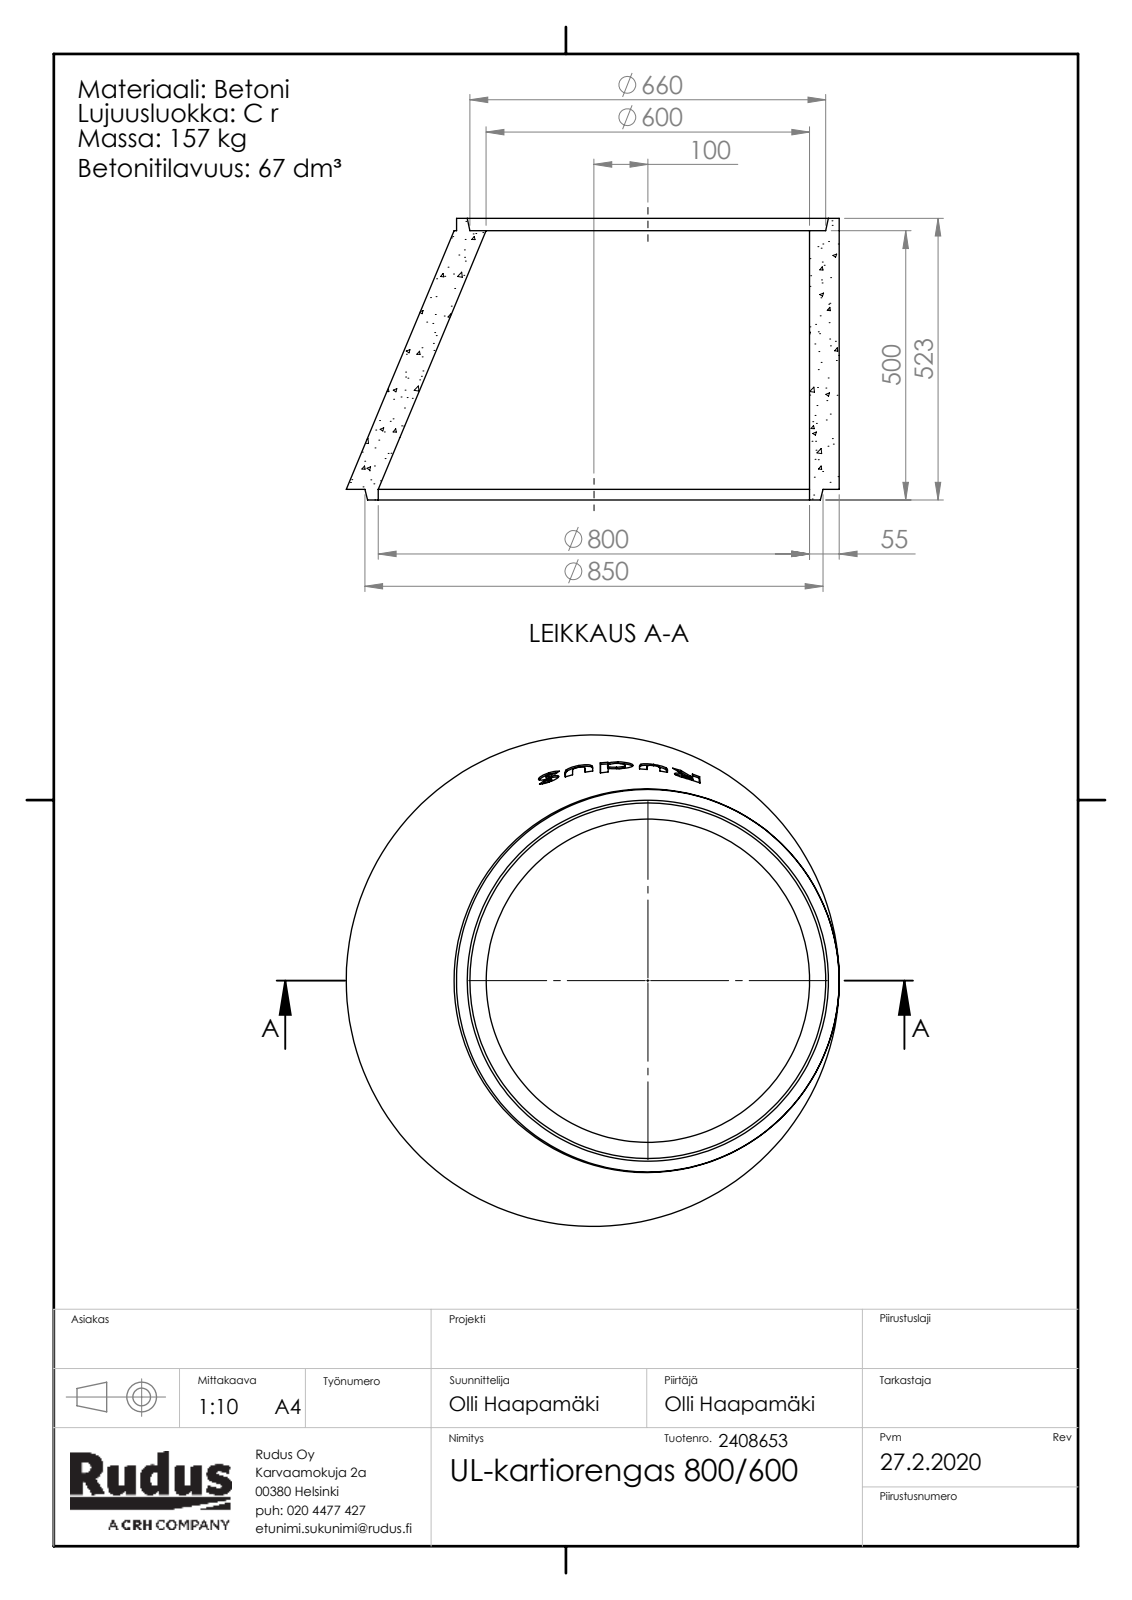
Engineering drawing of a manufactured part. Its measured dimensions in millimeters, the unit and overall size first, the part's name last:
Units: millimetres
Overall size (bounding box): 914.58 × 912.36 × 523
Round holes (diameter × count): ⌀800 ×1
Round bosses / shafts (diameter × count): ⌀710 ×1
Main face-to-face distances: 480, 20, 500, 523, 503, 23
Volume: 67 090 000 mm³ · Surface area: 2 810 000 mm²
Bodies: 1 solid, 94 faces (5 planar, 4 cylindrical, 85 other)
Part name (STEP PRODUCT): EK-osa-kaivorunko_UL-kaivonrengas; Rudus 2408653 UL-kartiorengas 800-600
STEP written by: SolidWorks 2019 (CONFIG_CONTROL_DESIGN)
